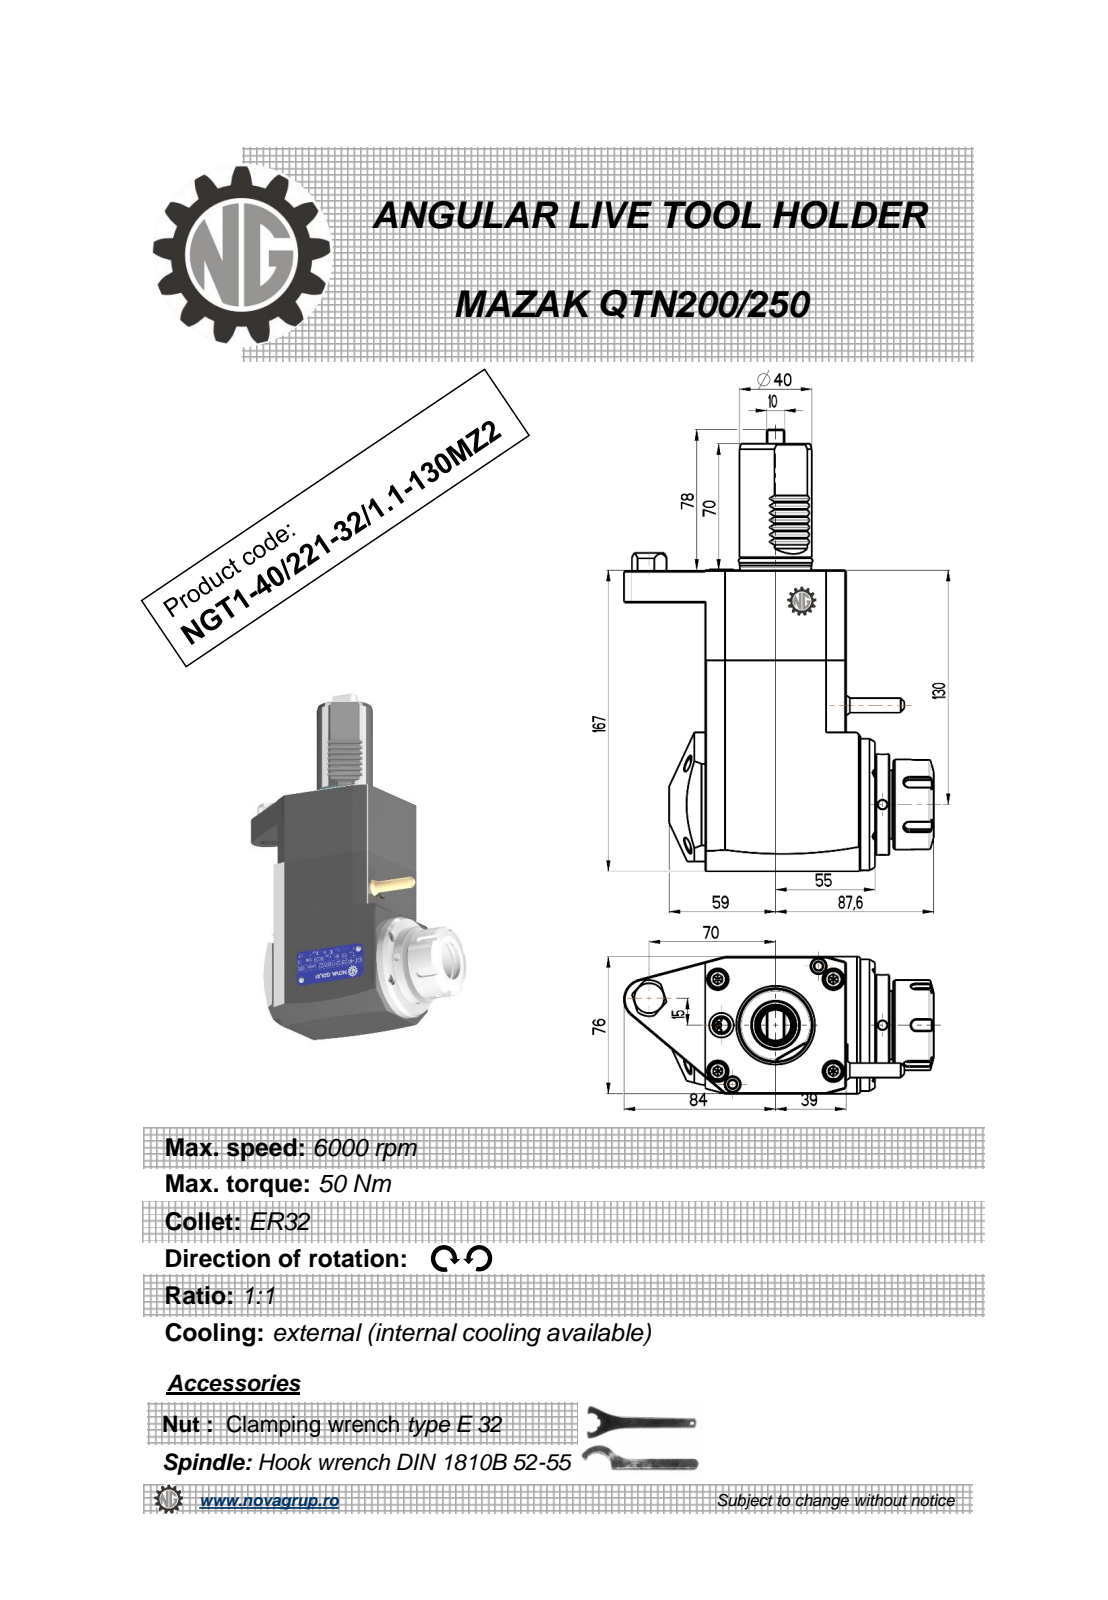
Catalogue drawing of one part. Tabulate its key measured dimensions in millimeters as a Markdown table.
| quantity | value |
| --- | --- |
| part name | NGT1_40_221_32_1_1_130MZ2 |
| STEP written by | PRO/ENGINEER BY PARAMETRIC TECHNOLOGY CORPORATION, 2010280 (CONFIG_CONTROL_DESIGN) |
| units | millimeters |
| bodies | 1 solid, 289 faces (132 planar, 74 cylindrical, 83 other) |
| overall size | 245 × 171.6 × 76 |
| volume | 1 284 000 mm³ |
| surface area | 91 859 mm² |
| round holes (diameter × count) | 5 × 3, 3 × 1, 8 × 1, 27 × 1 |
| round bosses / shafts (diameter × count) | 73 × 1, 56 × 1, 50 × 1, 43 × 1, 40 × 1, 39.4 × 1, 36.2 × 1, 10 × 1 |
| partial cylindrical surfaces (radius × count) | 0.3 × 7, 0.2 × 6, 3 × 5, 0.8 × 2, 300 × 2, 9 × 1, 10 × 1, 11.35 × 1 |
| main face-to-face distances | 76, 78, 167, 8, 16, 94, 18, 87.92, 149, 86 |
| hole center spacings | 60.42, 89.25 |
